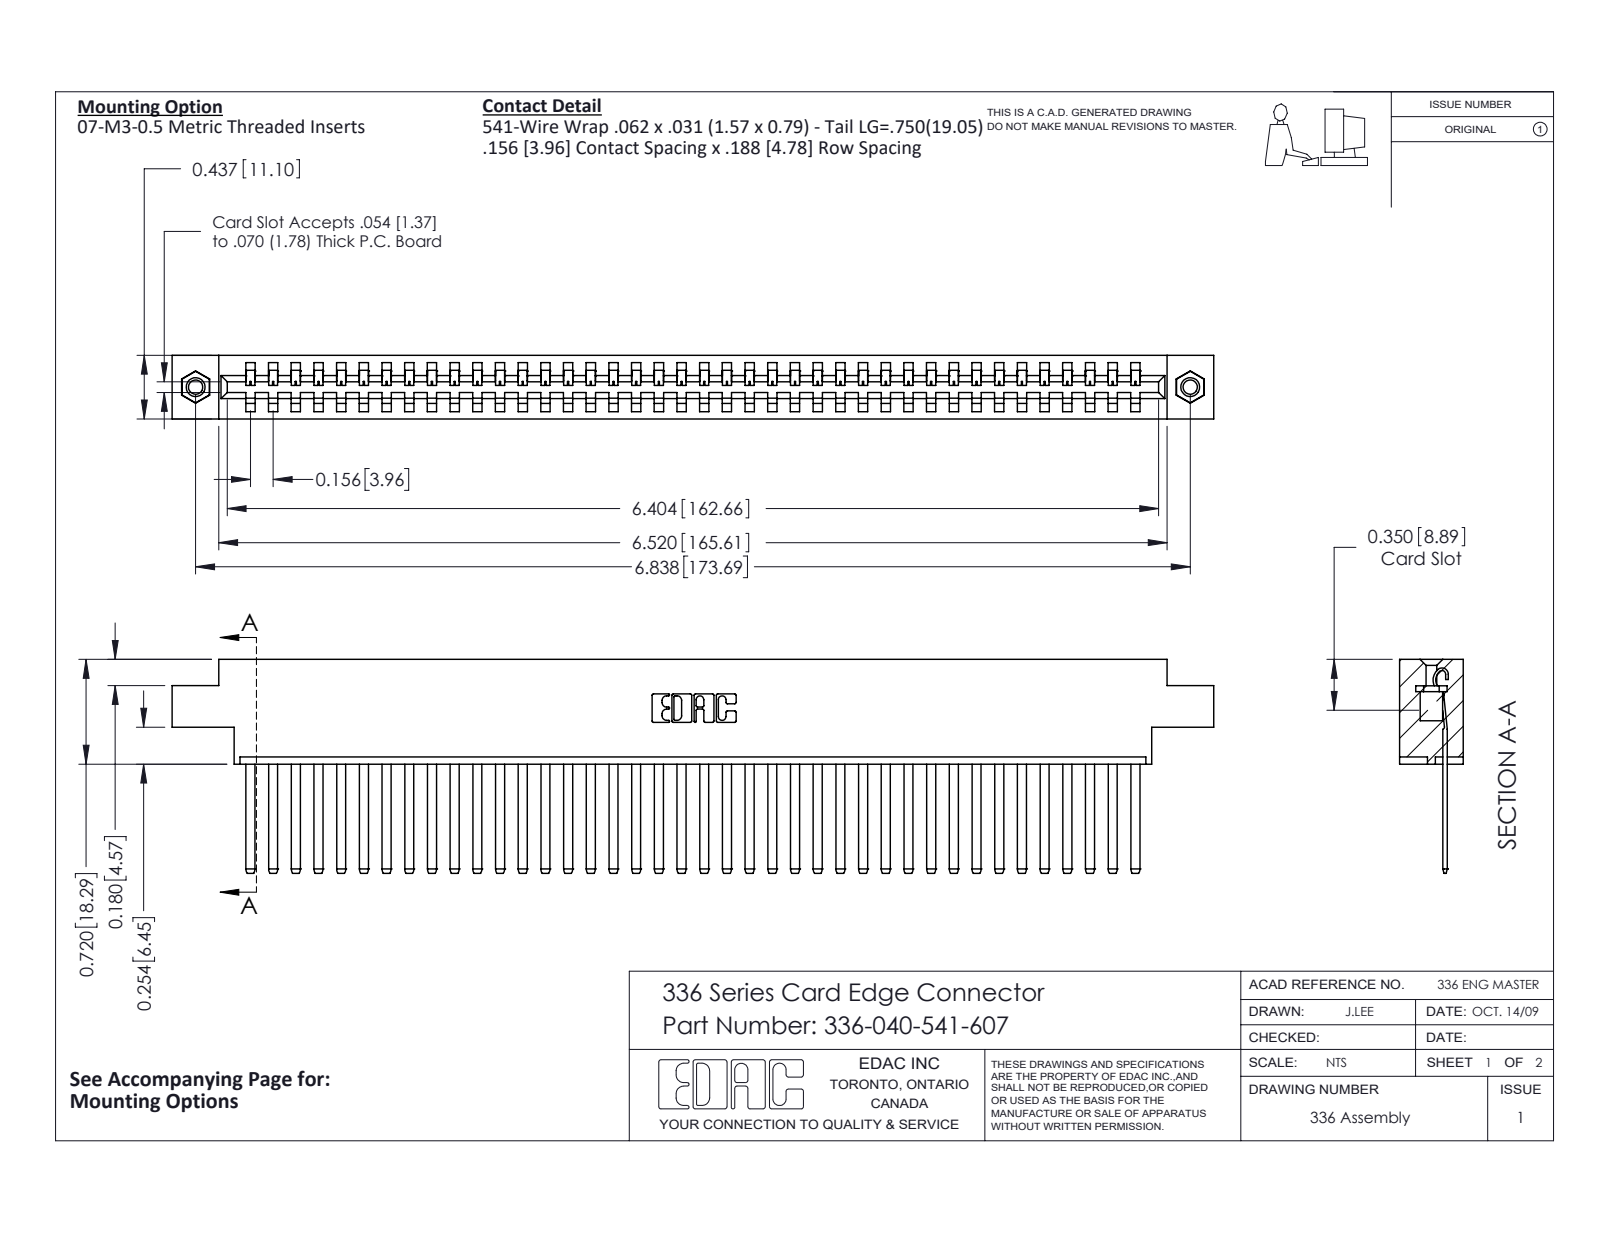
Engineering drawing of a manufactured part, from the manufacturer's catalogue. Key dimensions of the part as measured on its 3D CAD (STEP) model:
Part name (STEP PRODUCT): 345-250-001_345-250-005-103; 336 Part_Offset - .156 Dia - TI; 336-040-541-607; 336-290-001_336-290-541
STEP written by: SolidWorks 2020 (CONFIG_CONTROL_DESIGN)
Units: inches
Bodies: 43 solids, 2178 faces (1466 planar, 696 cylindrical, 16 other)
Overall size (bounding box): 7.161 × 1.47 × 0.437
Volume: 1.613 in³ · Surface area: 44.74 in²
Round holes (diameter × count): ⌀0.098 ×2, ⌀0.125 ×2, ⌀0.156 ×2
Round bosses / shafts (diameter × count): ⌀0.155 ×2
Partial cylindrical surfaces — rounded edges, fillets, slot ends (radius × count): R0.004 ×80, R0.056 ×80, R0.01 ×22, R0.007 ×6, R0.031 ×6, R0.026 ×3, R0.022 ×2, R0.04 ×2
Main face-to-face distances: 0.437, 0.181, 0.328, 0.14, 0.297, 0.109, 0.031, 0.256, 0.05, 0.131
Hole centre spacings: 6.838
